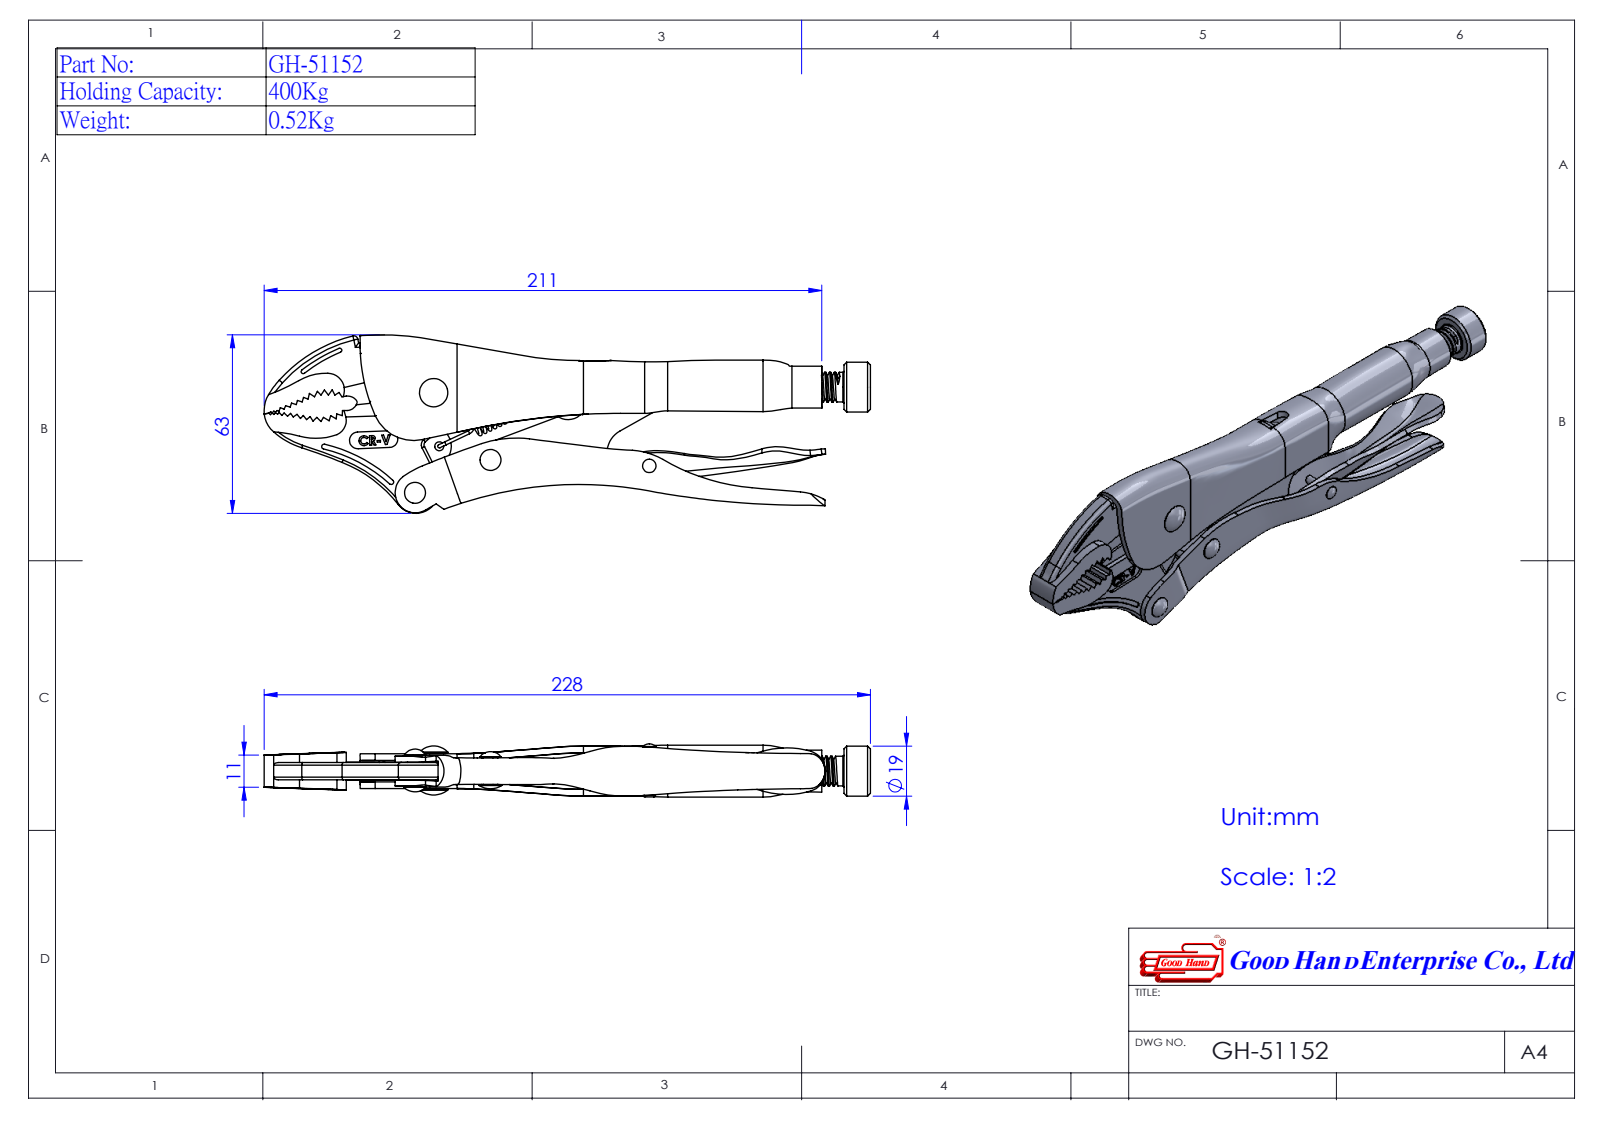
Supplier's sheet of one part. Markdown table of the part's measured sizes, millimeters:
| quantity | value |
| --- | --- |
| part name | GH-51152(簡化)-3; 310AI-上柄(實測版)-1^GH-51152(簡化)-3; Group1^GH-51152(簡化)-3 |
| STEP written by | SolidWorks 2016 (AUTOMOTIVE_DESIGN) |
| units | millimeters |
| bodies | 6 solids, 571 faces (149 planar, 232 cylindrical, 190 other) |
| overall size | 224.75 × 66.21 × 20.03 |
| volume | 69 082 mm³ |
| surface area | 52 340 mm² |
| round holes (diameter × count) | 3.34 × 1, 5.62 × 1, 7.47 × 1, 7.6 × 1, 10.6 × 1 |
| round bosses / shafts (diameter × count) | 7.8 × 2, 5.4 × 2, 1.2 × 2, 18.5 × 1, 11 × 1, 10.5 × 1, 8.2 × 1, 7.5 × 1 |
| partial cylindrical surfaces (radius × count) | 1 × 10, 1.5 × 6, 0.5 × 4, 0.75 × 2, 0.9 × 2, 3.1 × 2, 4 × 2, 0.35 × 1 |
| main face-to-face distances | 0.9, 5.5, 4.6, 6.4, 5.65, 1.05, 6.55, 6.7, 4.75, 1.8 |
| hole center spacings | 19.48, 20.01, 37.81 |
